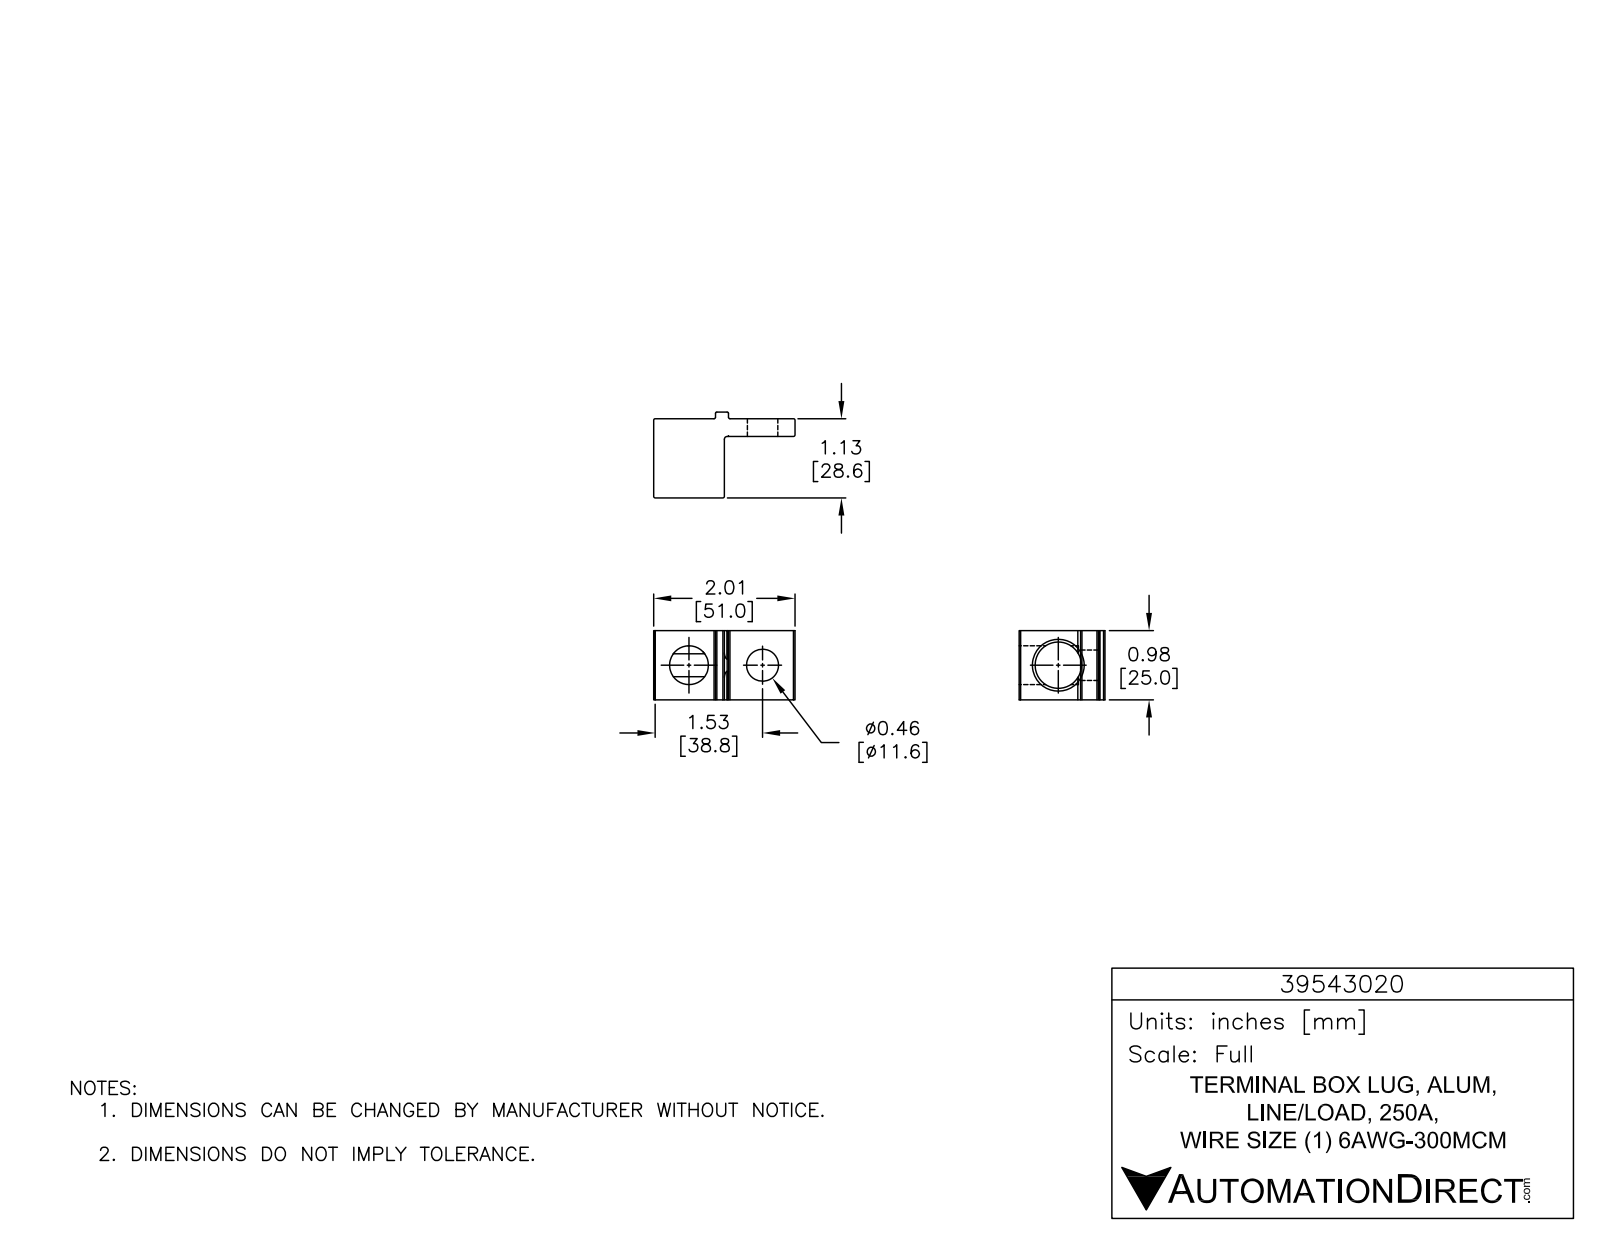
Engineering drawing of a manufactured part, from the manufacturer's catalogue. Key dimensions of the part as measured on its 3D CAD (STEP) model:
Part name (STEP PRODUCT): 39543020
STEP written by: SolidWorks 2015 (AUTOMOTIVE_DESIGN)
Units: inches
Bodies: 1 solid, 37 faces (15 planar, 20 cylindrical, 2 other)
Overall size (bounding box): 2.008 × 1.22 × 0.984
Volume: 0.934 in³ · Surface area: 10.52 in²
Round holes (diameter × count): ⌀0.433 ×1, ⌀0.551 ×1, ⌀0.657 ×1
Partial cylindrical surfaces — rounded edges, fillets, slot ends (radius × count): R0.02 ×9, R0.039 ×1
Main face-to-face distances: 0.984, 0.252, 1.126, 0.874, 1.004, 2.008, 0.094, 0.346, 1.22, 0.378
Hole centre spacings: 1.045
